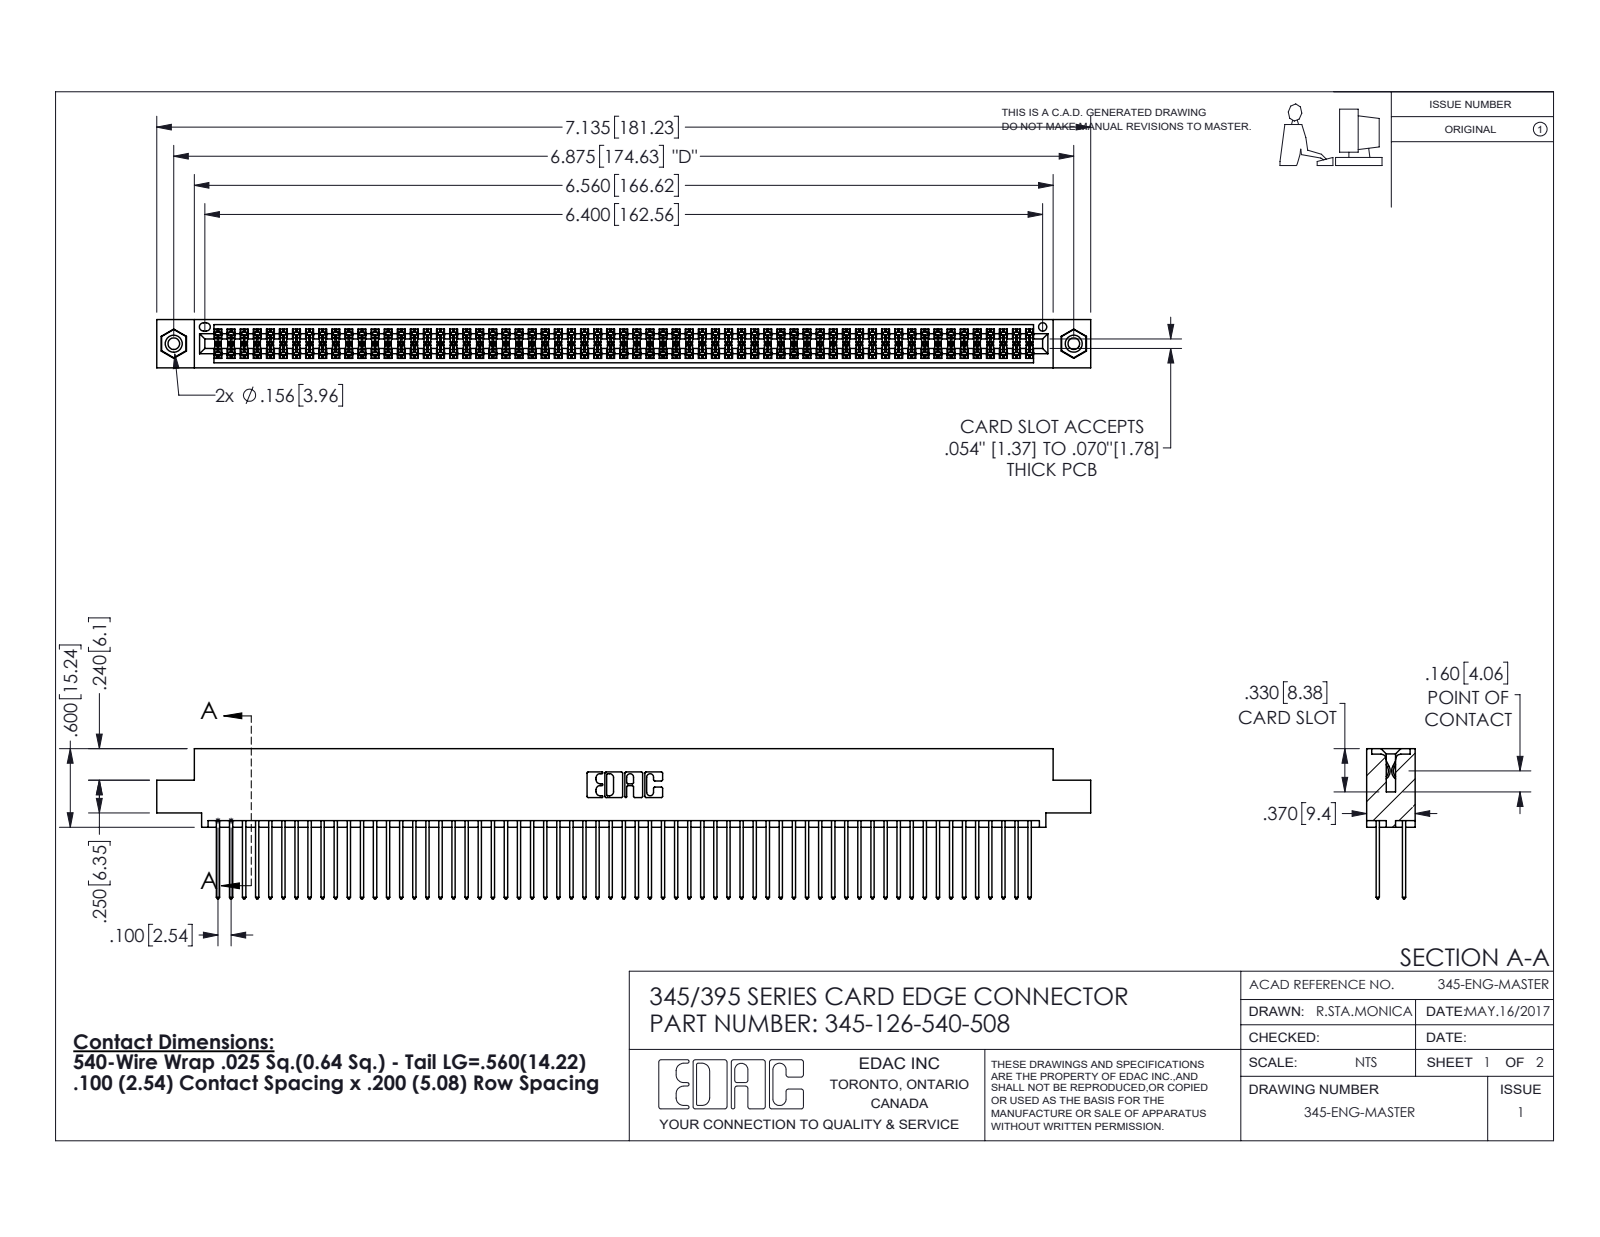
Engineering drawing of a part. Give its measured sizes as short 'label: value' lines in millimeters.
name: 345-292-001_345-293-140; 345-126-540-508; 345 Part_0.110 Offset - 0.156 Dia-TI; 345-250-001_345-250-003-102
written by: SolidWorks 2016 (CONFIG_CONTROL_DESIGN)
unit: mm
bodies: 129 solids, 6490 faces (4274 planar, 2200 cylindrical, 16 other)
size: 181.2 × 29.1 × 9.4
volume: 18 190 mm³; area: 29 630 mm²
holes: 2× ⌀2.3, 2× ⌀3.2, 2× ⌀4, 1× ⌀1.6
bosses: 2× ⌀3.9
rounds: 189× R0.2, 126× R0.3, 22× R0.3, 6× R0.2, 6× R0.8, 3× R0.7, 2× R0.4, 2× R0.5
face distances: 1.8, 7.6, 5.1, 2.5, 6.9, 0.6, 5.7, 9.4, 4.4, 3.8
hole spacings: 6.9, 168.6, 174.6
